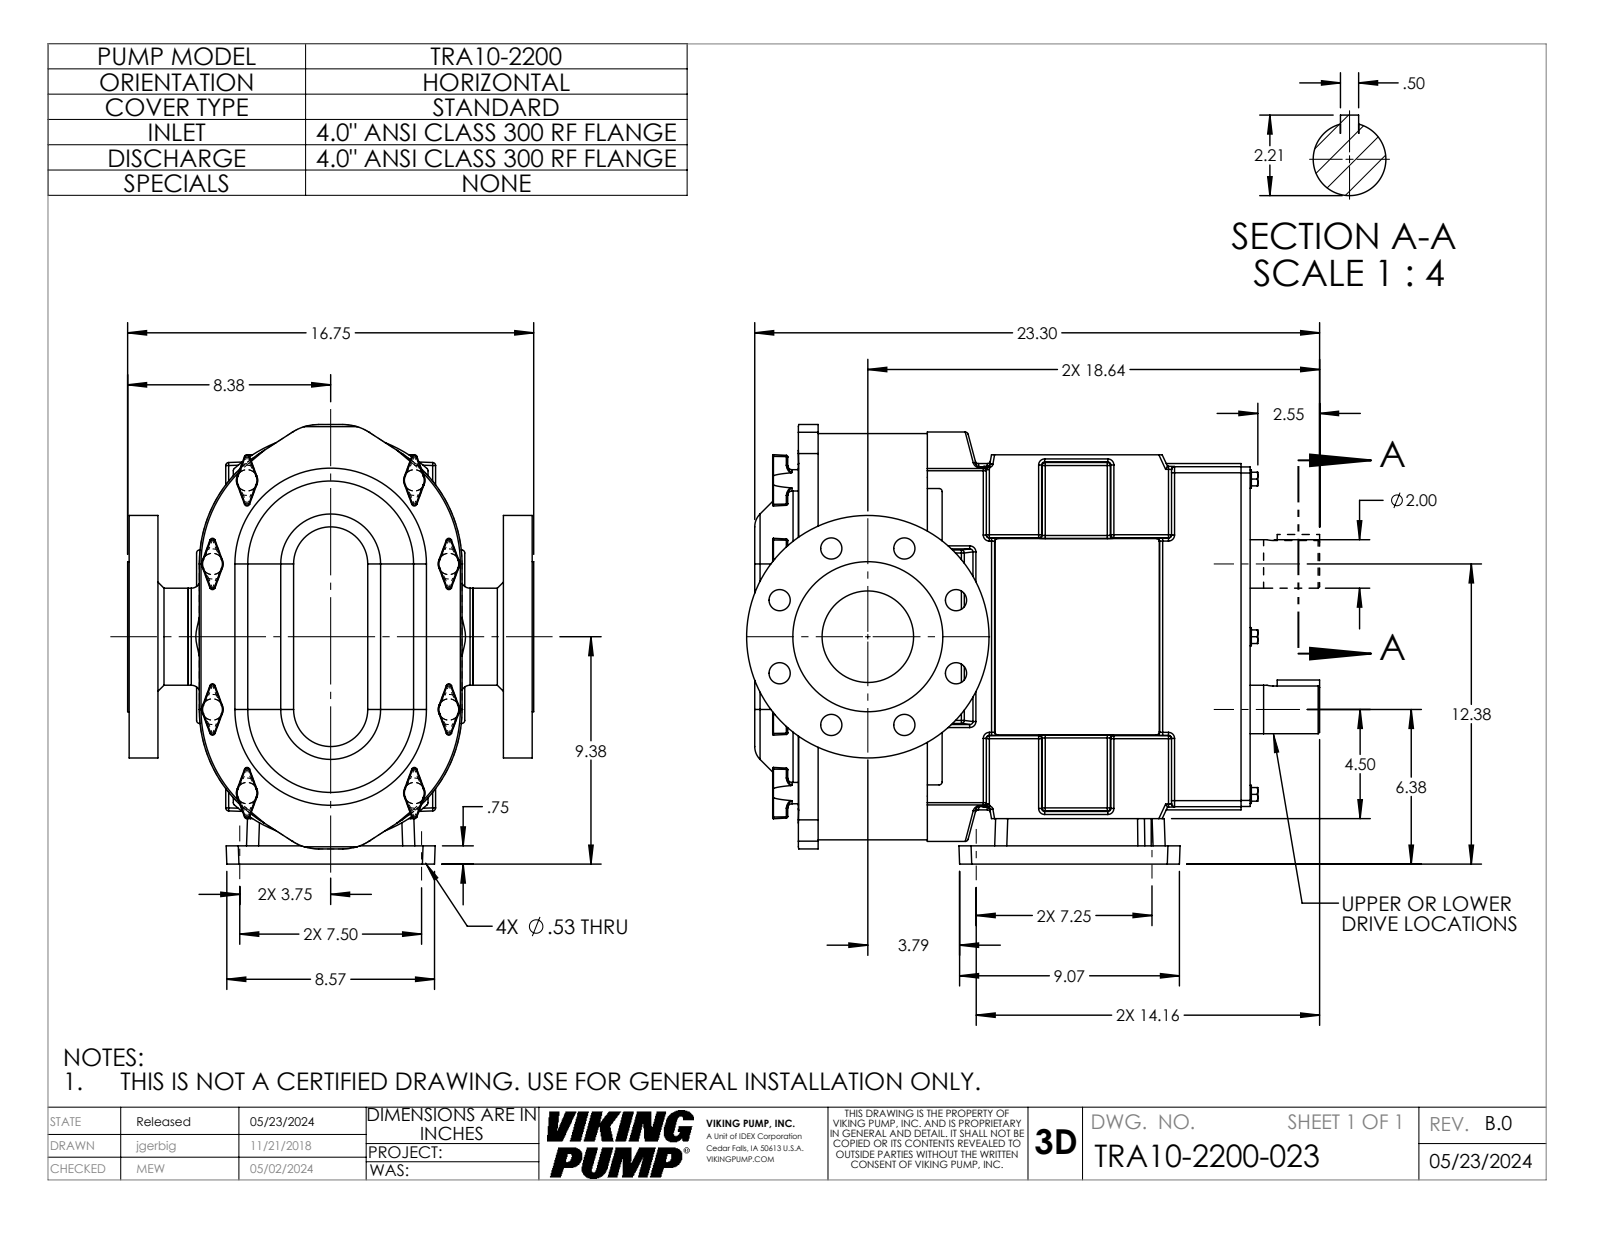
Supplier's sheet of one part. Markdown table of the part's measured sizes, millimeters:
| quantity | value |
| --- | --- |
| part name | TRA10-2200-COVER-STD; 2200FLG300-40; TRA10-2200-GEARBOX-H; TRA10-2200-023 (+1 more) |
| STEP written by | SolidWorks 2023 (AUTOMOTIVE_DESIGN) |
| units | millimeters |
| bodies | 5 solids, 950 faces (266 planar, 376 cylindrical, 308 other) |
| overall size | 600.4 × 460.4 × 425.5 |
| volume | 45 410 000 mm³ |
| surface area | 1 668 000 mm² |
| round holes (diameter × count) | 22.2 × 8, 13.5 × 4, 95.9 × 1, 95.9 × 1 |
| round bosses / shafts (diameter × count) | 22.4 × 8, 19.1 × 6, 50.8 × 2, 254 × 1, 157.1 × 1, 101.6 × 1 |
| partial cylindrical surfaces (radius × count) | 3.2 × 138, 0.8 × 32, 1.5 × 32, 6.4 × 16, 12.7 × 16, 19.1 × 4, 50.8 × 4, 136.5 × 2 |
| main face-to-face distances | 114.4, 79, 283, 66.7, 295.3, 12.3, 216.3, 452.6, 338.2, 30.2 |
| hole center spacings | 184.8, 100, 76.5, 76.6, 141.5, 100, 141.4, 141.5 |
